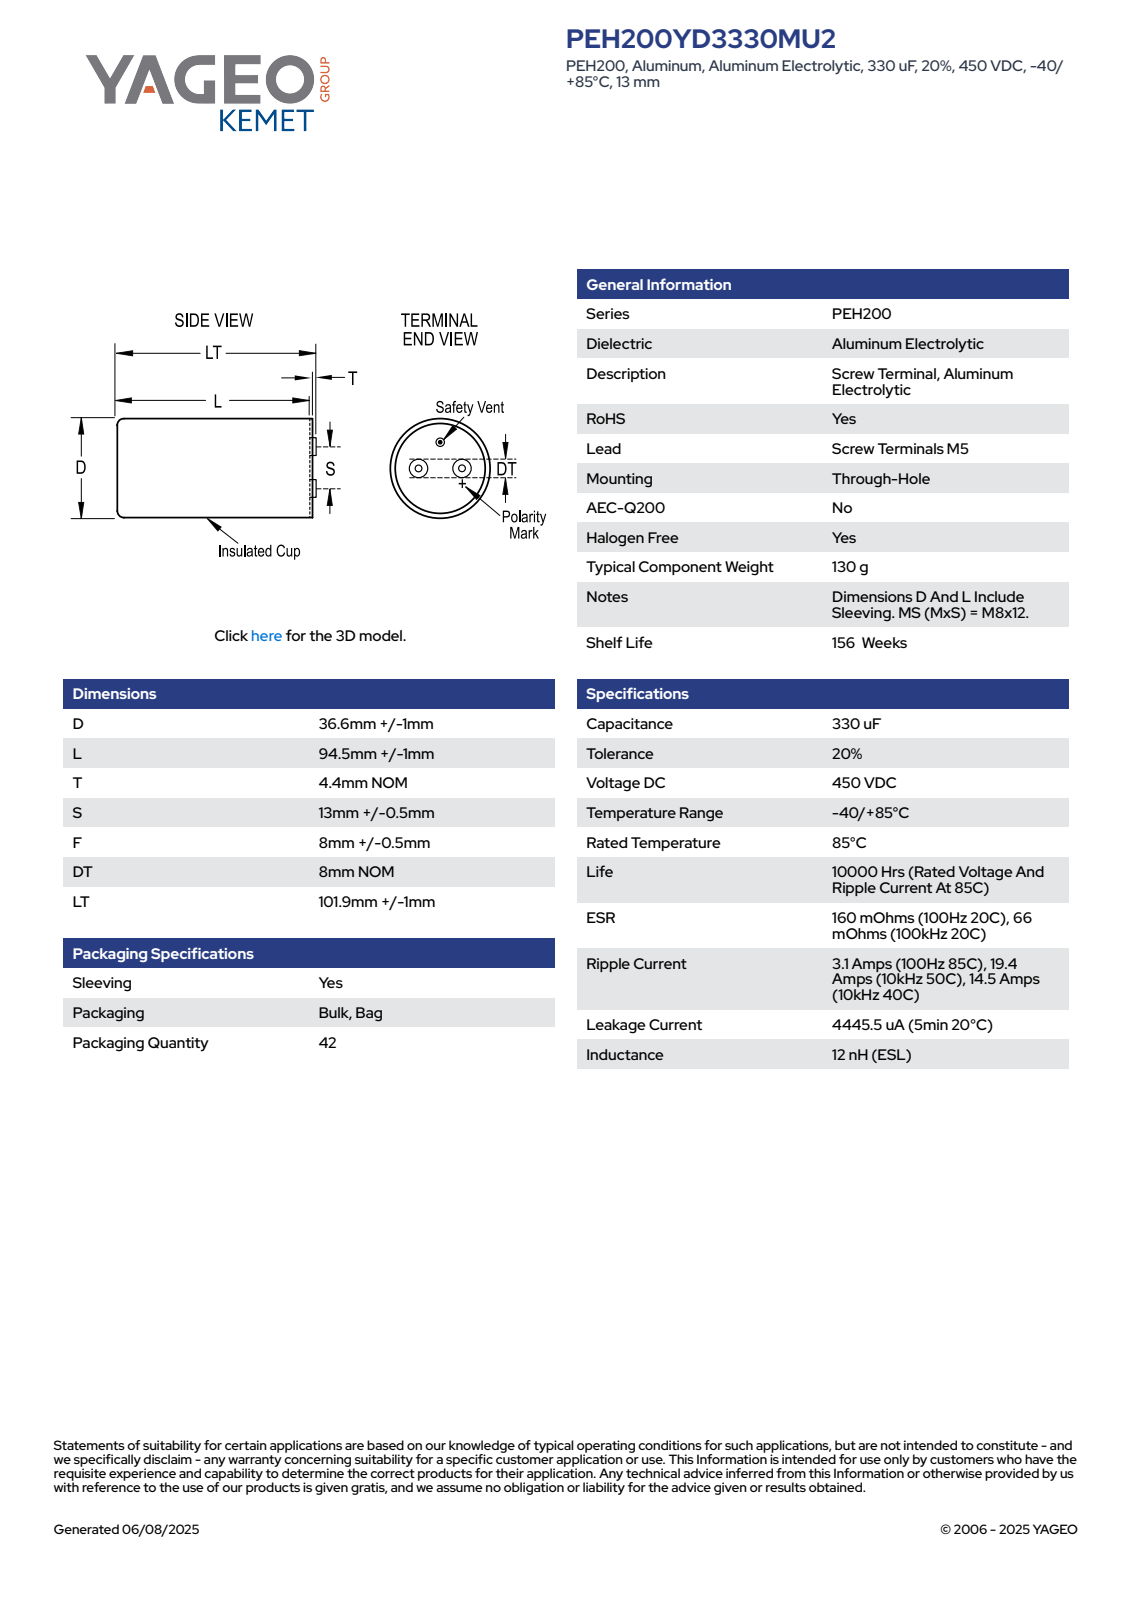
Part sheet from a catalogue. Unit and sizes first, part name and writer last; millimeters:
Units: millimetres
Overall size (bounding box): 102.9 × 37.6 × 37.6
Round holes (diameter × count): ⌀5 ×2, ⌀35.6 ×1
Round bosses / shafts (diameter × count): ⌀8 ×2, ⌀37.6 ×1
Partial cylindrical surfaces — rounded edges, fillets, slot ends (radius × count): R18.79 ×1
Main face-to-face distances: 95.5, 3, 98.5, 4.4, 7.4, 102.9, 17.51, 13.11, 10.11, 85.39
Hole centre spacings: 6.5, 13
Volume: 106 450 mm³ · Surface area: 14 711 mm²
Bodies: 3 solids, 77 faces (30 planar, 15 cylindrical, 32 other)
Part name (STEP PRODUCT): CARC_D37.6L95.5S13T4.4; Round_Terminal; Can_Round_4
STEP written by: SolidWorks 2014 (AUTOMOTIVE_DESIGN)
